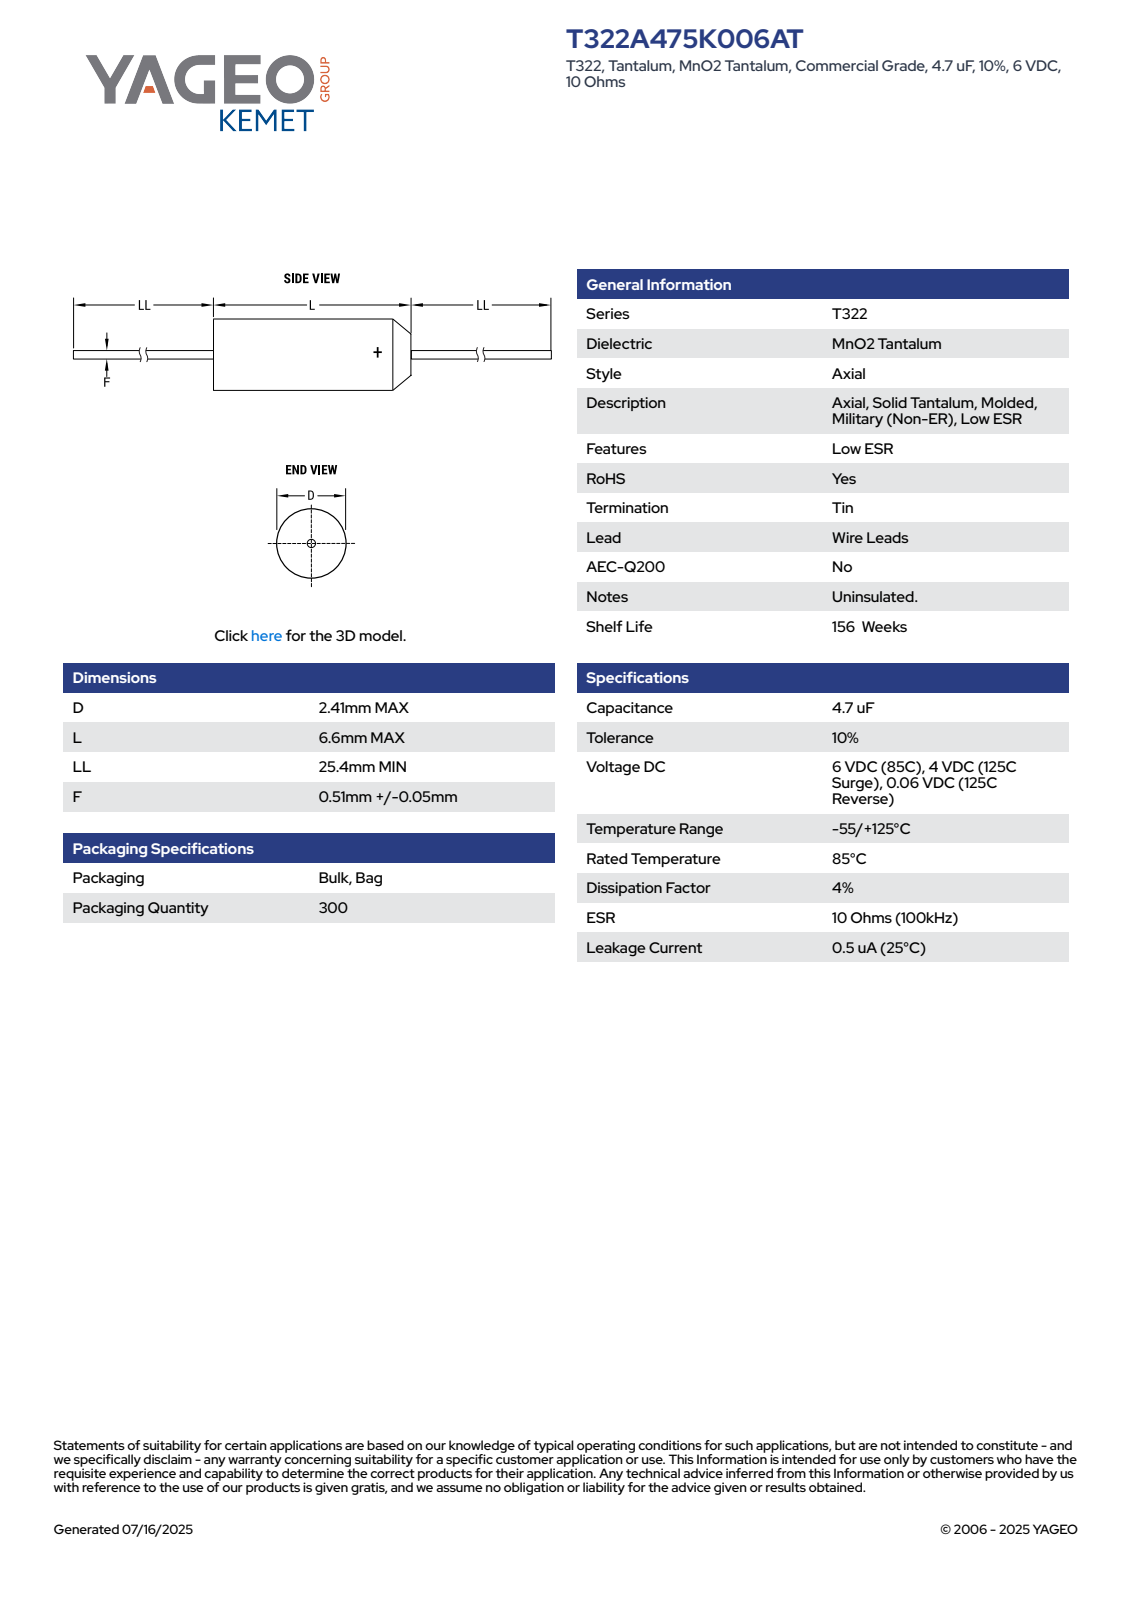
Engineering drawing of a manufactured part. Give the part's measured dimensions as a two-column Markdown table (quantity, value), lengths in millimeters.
| quantity | value |
| --- | --- |
| part name | CTAM_D2.41L6.6LL25.4F0.56 |
| STEP written by | SolidWorks 2020 (AUTOMOTIVE_DESIGN) |
| units | millimeters |
| bodies | 1 solid, 102 faces (38 planar, 25 cylindrical, 39 other) |
| overall size | 57.4 × 2.41 × 2.41 |
| volume | 41 mm³ |
| surface area | 144 mm² |
| round bosses / shafts (diameter × count) | 2.41 × 1, 0.56 × 1 |
| partial cylindrical surfaces (radius × count) | 1.2 × 1 |
| main face-to-face distances | 6.6, 25.4, 32, 57.4, 30.3, 4.9, 1.7, 27.1, 30.4, 5 |
